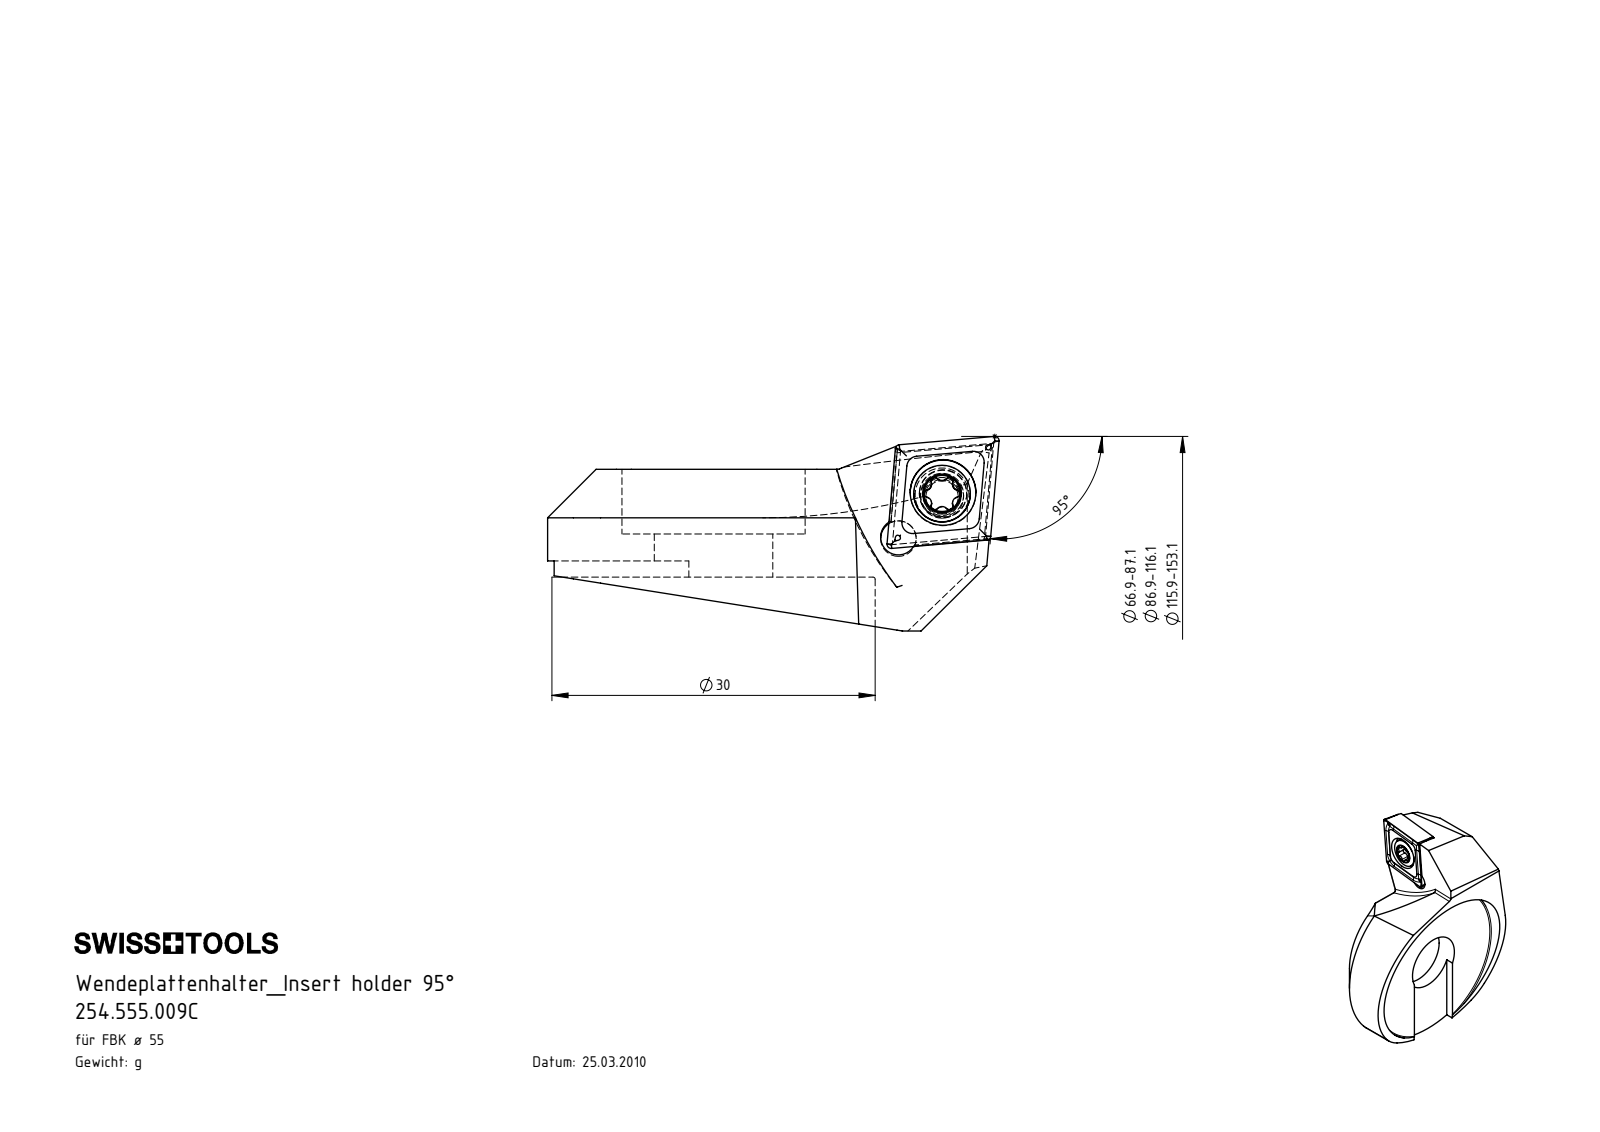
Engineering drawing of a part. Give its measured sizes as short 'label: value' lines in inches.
name: 254.555.009C; F55-WCB.002.013_D_fertigbearbeitet; CCMT09T304; WCB-ER2.001.009_A
written by: SolidWorks 2017 (CONFIG_CONTROL_DESIGN)
unit: in
bodies: 5 solids, 156 faces (50 planar, 46 cylindrical, 60 other)
size: 1.65 × 1.303 × 0.711
volume: 0.5 in³; area: 7.81 in²
holes: 2× ⌀0.13, 1× ⌀0.173, 1× ⌀0.24, 1× ⌀0.433, 1× ⌀0.669, 1× ⌀1.181
bosses: 1× ⌀0.207, 1× ⌀0.157
rounds: 6× R0.013, 6× R0.023, 2× R0.02, 2× R0.394, 1× R0.065, 1× R0.652, 1× R0.823, 1× R1.181
face distances: 0.394, 0.354, 0.039, 0.148, 0.197, 0.236, 0.157, 0.335, 0.295, 0.098
hole spacings: 0.226, 0.231
